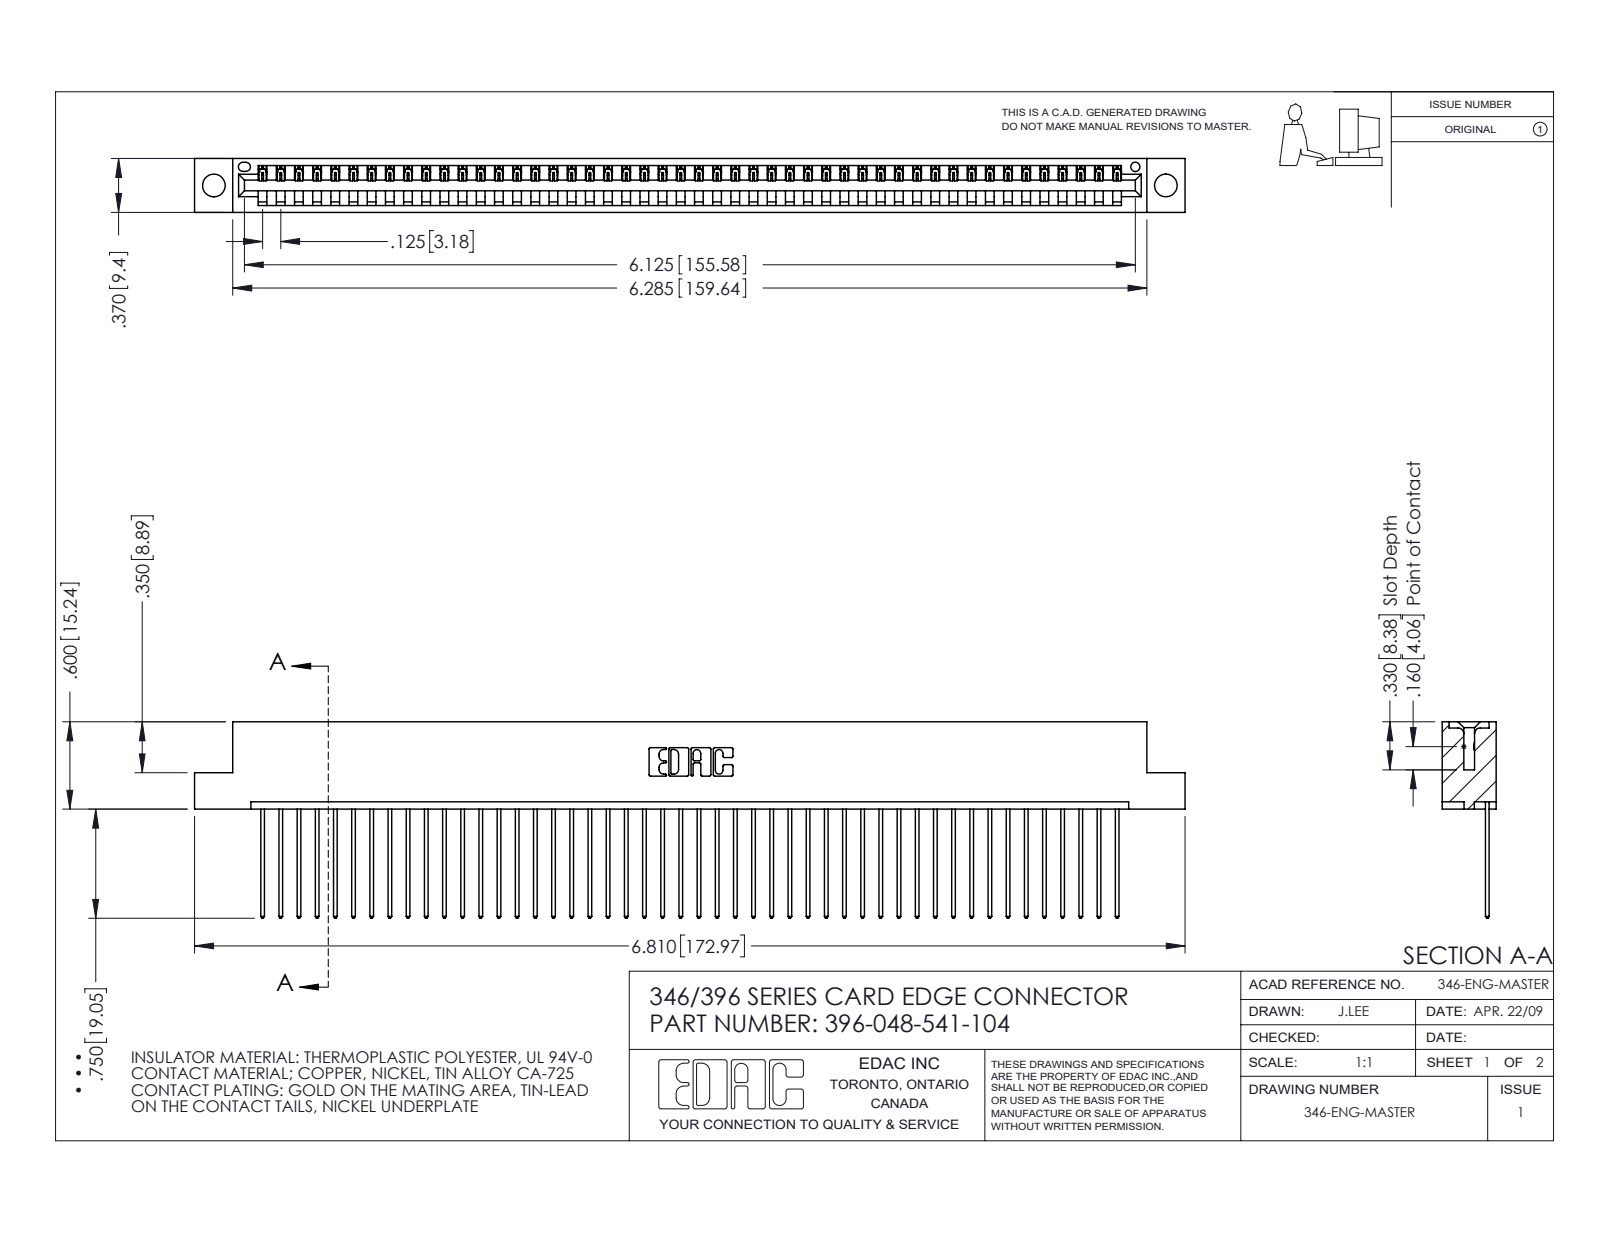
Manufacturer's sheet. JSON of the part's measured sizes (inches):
{"part_name": "346 Part_Flush Mounting Lugs - 0.156 Dia-TH; 396-048-541-104; 345-292-001_345-293-141", "step_written_by": "SolidWorks 2016 (CONFIG_CONTROL_DESIGN)", "units": "inches", "bodies": {"solids": 49, "faces": 2906, "planar": 1996, "cylindrical": 910, "other": 0}, "overall_size": [6.81, 1.35, 0.37], "volume_in3": 1.017, "surface_area_in2": 33.56, "round_holes": [[0.156, 2], [0.064, 1]], "partial_cylinders_radius": [[0.006, 96], [0.01, 96], [0.01, 22], [0.007, 6], [0.031, 6], [0.026, 3], [0.031, 2], [0.04, 2]], "face_to_face_distances": [0.048, 0.322, 0.37, 0.25, 0.072, 0.298, 0.025, 0.148, 0.222, 0.1], "hole_center_spacings": [0.246, 6.336, 6.545]}
